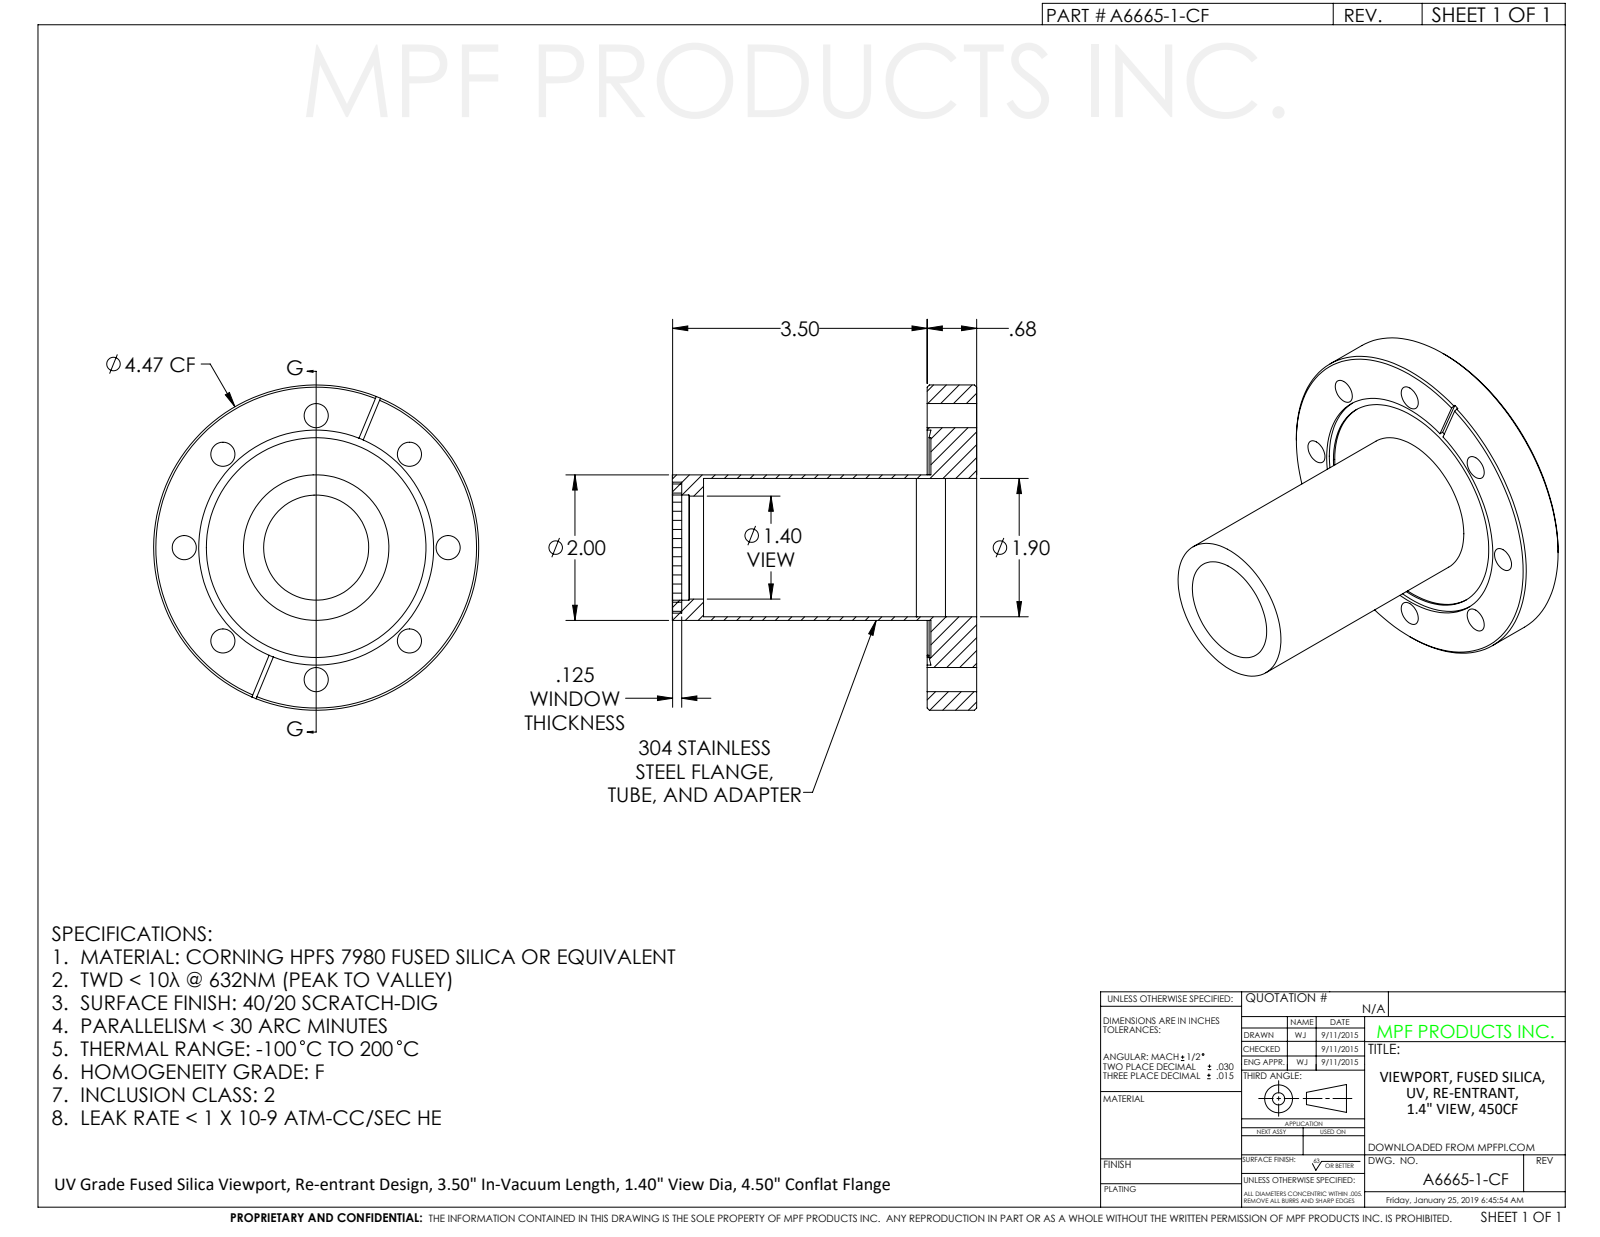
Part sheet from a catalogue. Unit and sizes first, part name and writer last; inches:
Units: inches
Overall size (bounding box): 4.47 × 4.47 × 4.18
Round holes (diameter × count): ⌀0.332 ×8, ⌀1.42 ×1, ⌀1.745 ×1, ⌀1.8 ×1, ⌀1.902 ×1, ⌀2.16 ×1, ⌀3.02 ×1, ⌀3.23 ×1
Round bosses / shafts (diameter × count): ⌀4.47 ×1, ⌀2.035 ×1, ⌀2 ×1, ⌀1.896 ×1, ⌀1.765 ×1, ⌀1.48 ×1, ⌀1.44 ×1
Main face-to-face distances: 0.68, 0.629, 0.051, 4.18, 3.551, 3.5, 4.055, 3.426, 3.375, 0.125
Hole centre spacings: 1.389, 1.814, 3.352, 2.565, 2.566, 3.628, 3.628
Volume: 9.614 in³ · Surface area: 98.35 in²
Bodies: 1 solid, 72 faces (14 planar, 44 cylindrical, 14 other)
Part name (STEP PRODUCT): A6665-1-CF
STEP written by: SolidWorks 2011 (CONFIG_CONTROL_DESIGN)
